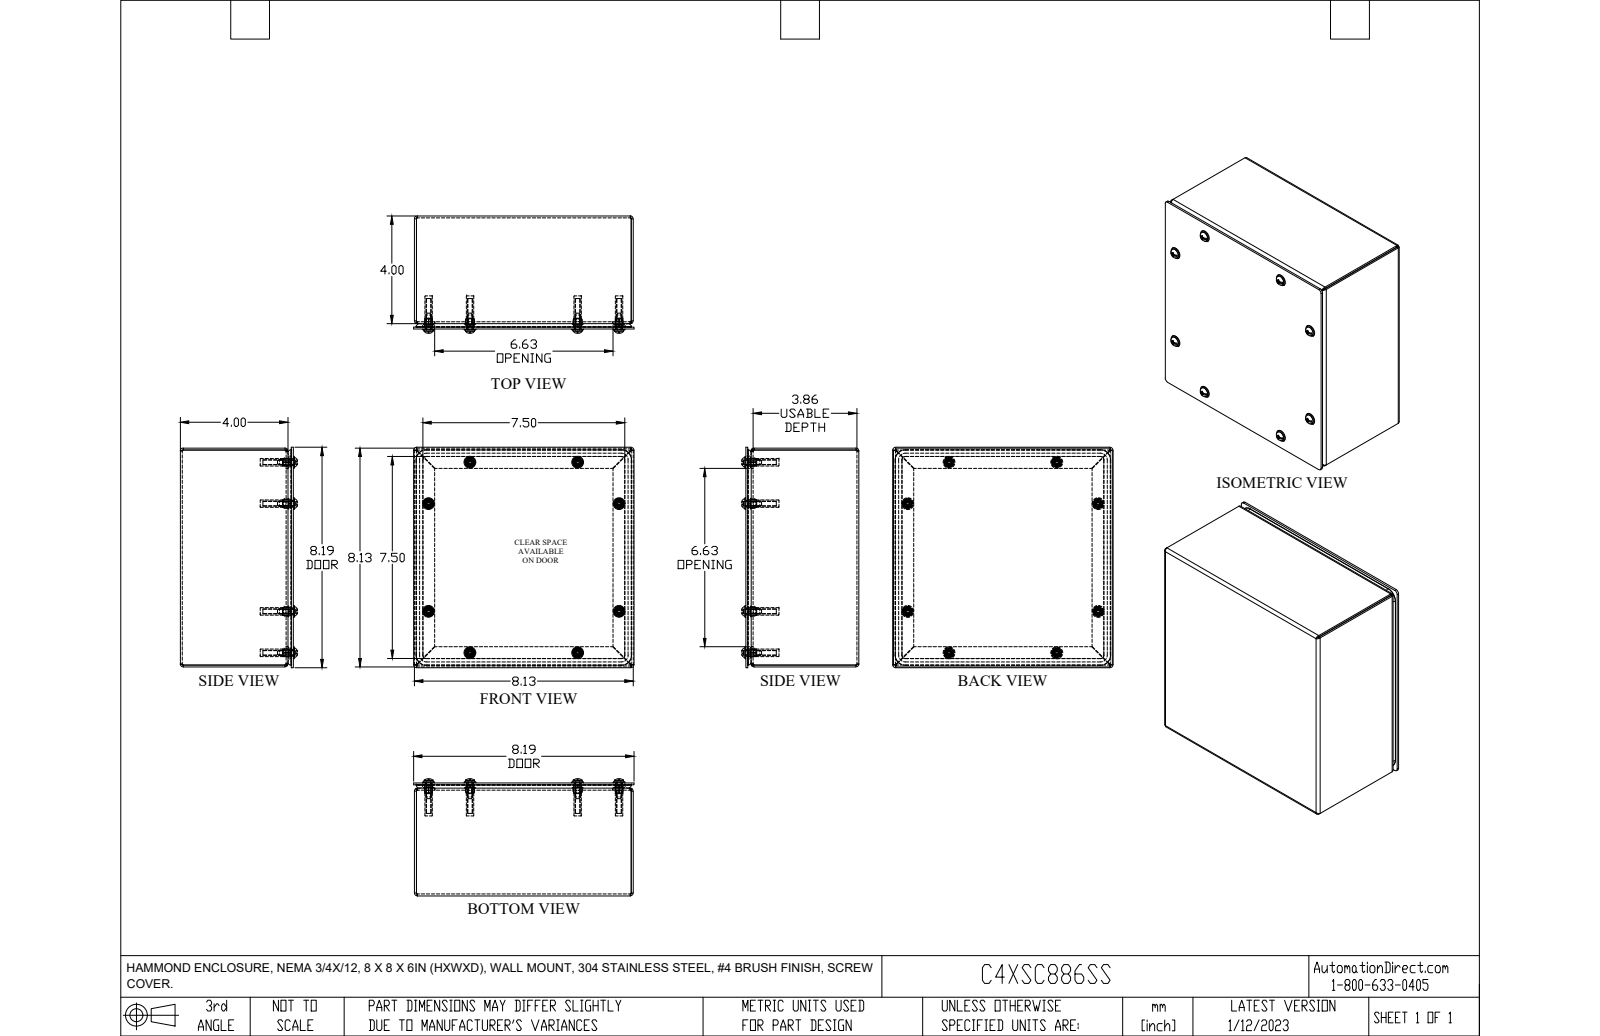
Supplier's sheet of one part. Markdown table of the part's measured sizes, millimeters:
| quantity | value |
| --- | --- |
| part name | C3SC886GY |
| STEP written by | SolidWorks 2021 (AUTOMOTIVE_DESIGN) |
| units | millimeters |
| bodies | 27 solids, 780 faces (480 planar, 152 cylindrical, 148 other) |
| overall size | 208 × 208 × 161.2 |
| volume | 414 400 mm³ |
| surface area | 481 200 mm² |
| round holes (diameter × count) | 4 × 8, 4.1 × 8, 6.4 × 8 |
| round bosses / shafts (diameter × count) | 11.2 × 8, 9.9 × 8, 6.1 × 8, 4.8 × 8, 3.8 × 8, 7 × 4, 7 × 4 |
| partial cylindrical surfaces (radius × count) | 1 × 8, 2.8 × 8, 3.2 × 8, 4.1 × 8, 3.2 × 4, 9.5 × 4 |
| main face-to-face distances | 1.8, 206.5, 1.8, 204.7, 204.7, 202.9, 1.8, 155.6, 157.4, 153.8 |
| hole center spacings | 146, 55.2, 101.6, 179.7, 198.9, 206.4 |
